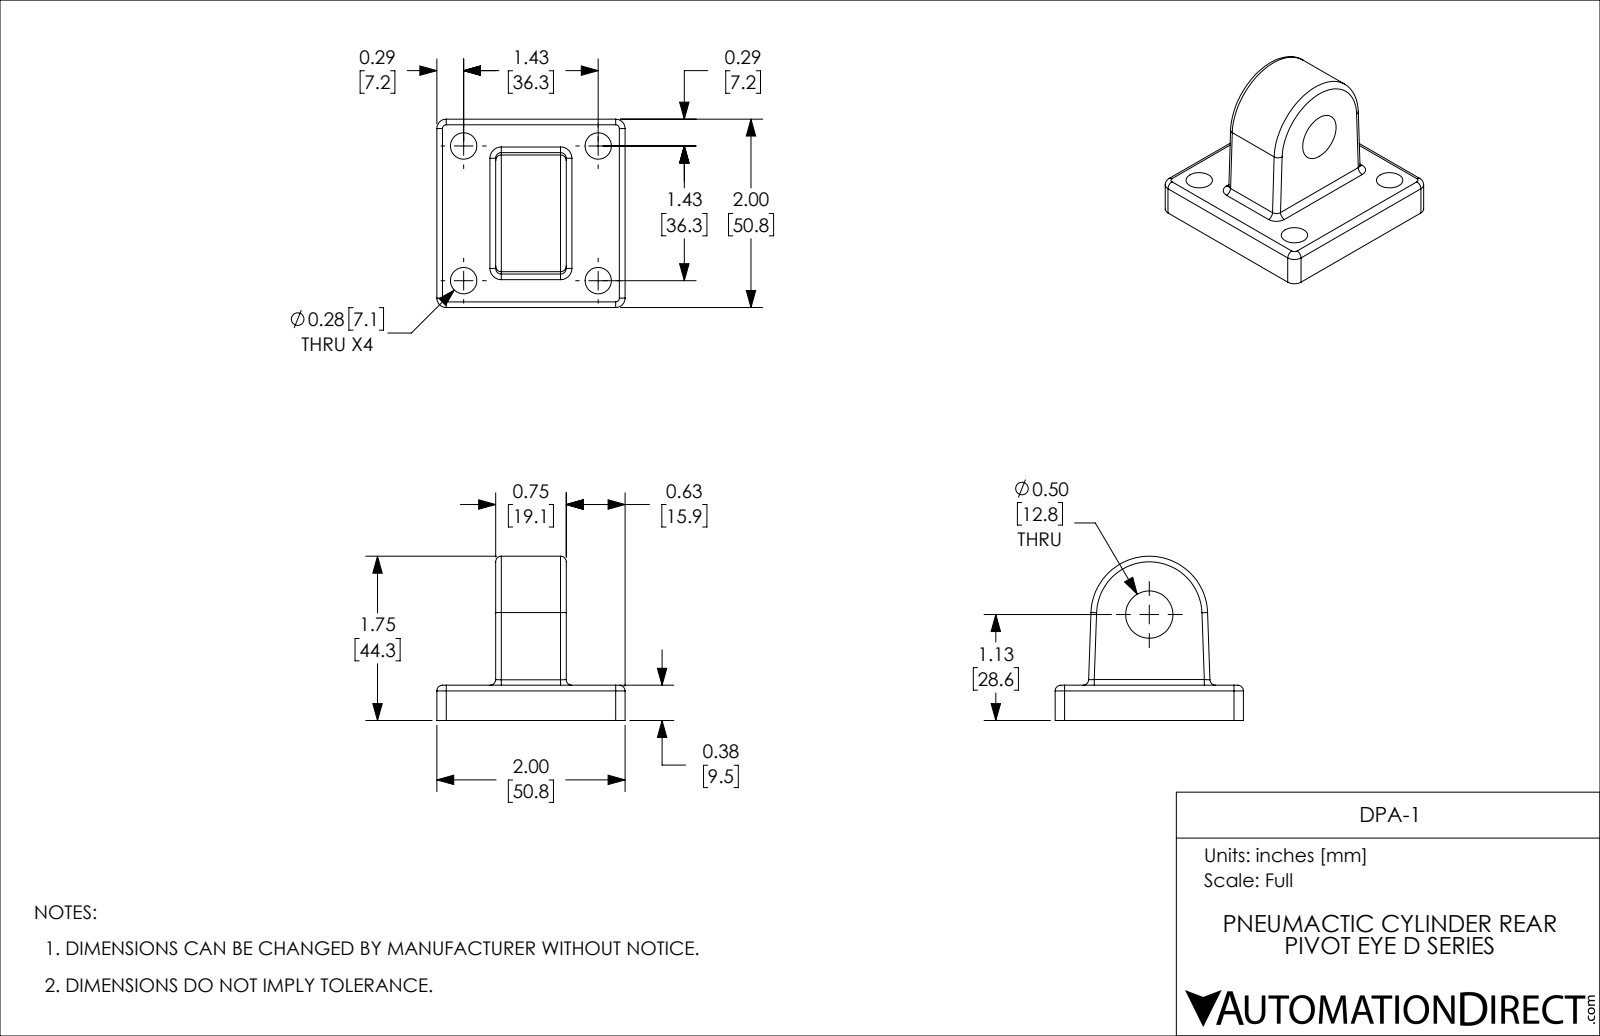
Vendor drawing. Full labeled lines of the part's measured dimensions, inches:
Part name (STEP PRODUCT): DPA-1
STEP written by: SolidWorks 2018 (AUTOMOTIVE_DESIGN)
Units: inches
Bodies: 1 solid, 48 faces (10 planar, 28 cylindrical, 10 other)
Overall size (bounding box): 2 × 2 × 1.745
Volume: 2.413 in³ · Surface area: 16.78 in²
Round holes (diameter × count): ⌀0.28 ×4, ⌀0.502 ×1
Partial cylindrical surfaces — rounded edges, fillets, slot ends (radius × count): R0.06 ×12, R0.1 ×4, R0.62 ×1
Main face-to-face distances: 0.375, 0.625, 1.375, 2, 0.75
Hole centre spacings: 1.43, 2.022
